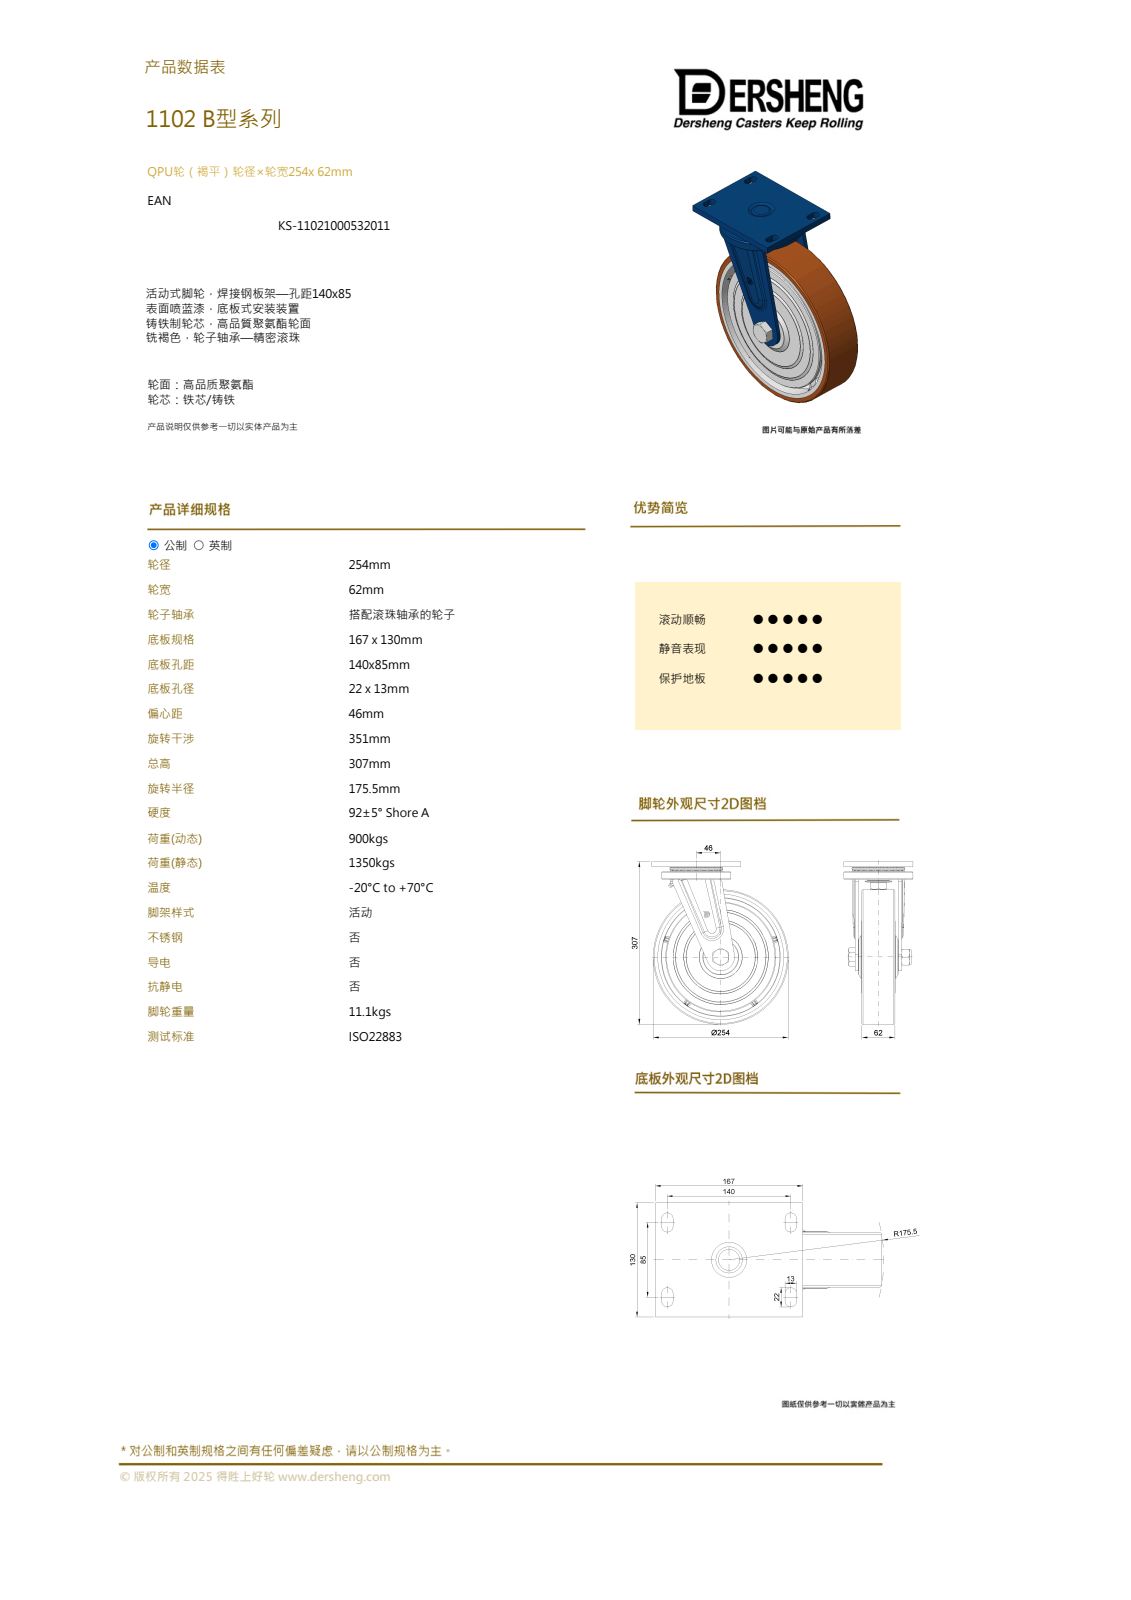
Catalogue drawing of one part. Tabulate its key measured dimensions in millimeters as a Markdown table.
| quantity | value |
| --- | --- |
| part name | PRT0002 |
| STEP written by | CREO PARAMETRIC BY PTC INC, 2024325 (CONFIG_CONTROL_DESIGN) |
| units | millimeters |
| bodies | 0 solids, 170 faces (60 planar, 8 cylindrical, 102 other) |
| overall size | 307 × 256.5 × 130 |
| round bosses / shafts (diameter × count) | 254 × 1, 130 × 1, 19.8 × 1 |
| partial cylindrical surfaces (radius × count) | 5 × 1 |
| main face-to-face distances | 2, 61, 6, 6.5, 68, 0.5, 74.5, 4, 63, 59 |
